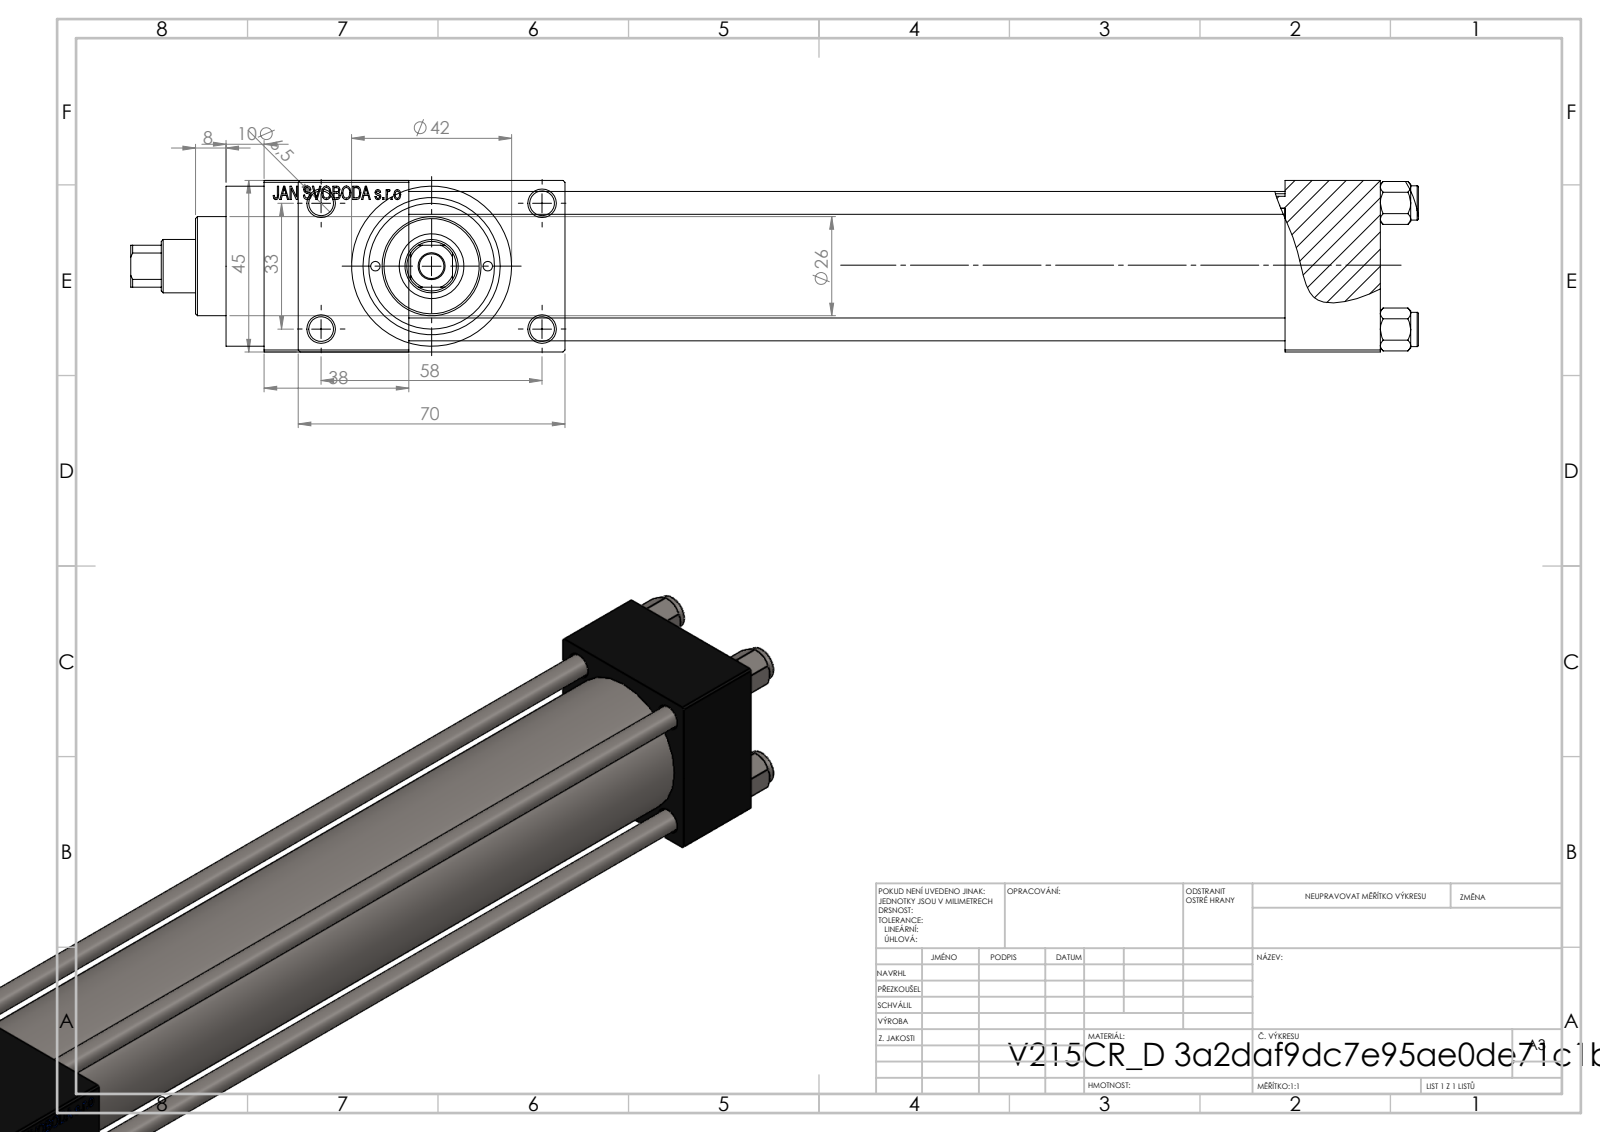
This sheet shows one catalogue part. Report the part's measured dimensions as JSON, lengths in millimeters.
{"part_name": "V215_VC_A; V215CR_D_TYCINKA; NUT_M5_D; V215CR_D_Body (+1 more)", "step_written_by": "SolidWorks 2019 (CONFIG_CONTROL_DESIGN)", "units": "millimeters", "bodies": {"solids": 11, "faces": 1110, "planar": 498, "cylindrical": 92, "other": 520}, "overall_size": [338, 70, 45], "volume_mm3": 337600, "surface_area_mm2": 136451, "round_holes": [[6.5, 5], [6, 4], [2.5, 2], [7, 2], [13.16, 2], [20, 2], [14, 1], [17, 1], [24, 1], [32, 1], [33, 1]], "round_bosses_or_shafts": [[9, 4], [42, 1], [38, 1], [26, 1]], "partial_cylinders_radius": [[6.5, 1]], "face_to_face_distances": [45, 25, 12.5, 230, 255, 57.5, 268, 38, 293, 70], "hole_center_spacings": [12.4, 16.7, 21.8, 23.48, 33.2, 33.37, 35.35, 35.47]}
